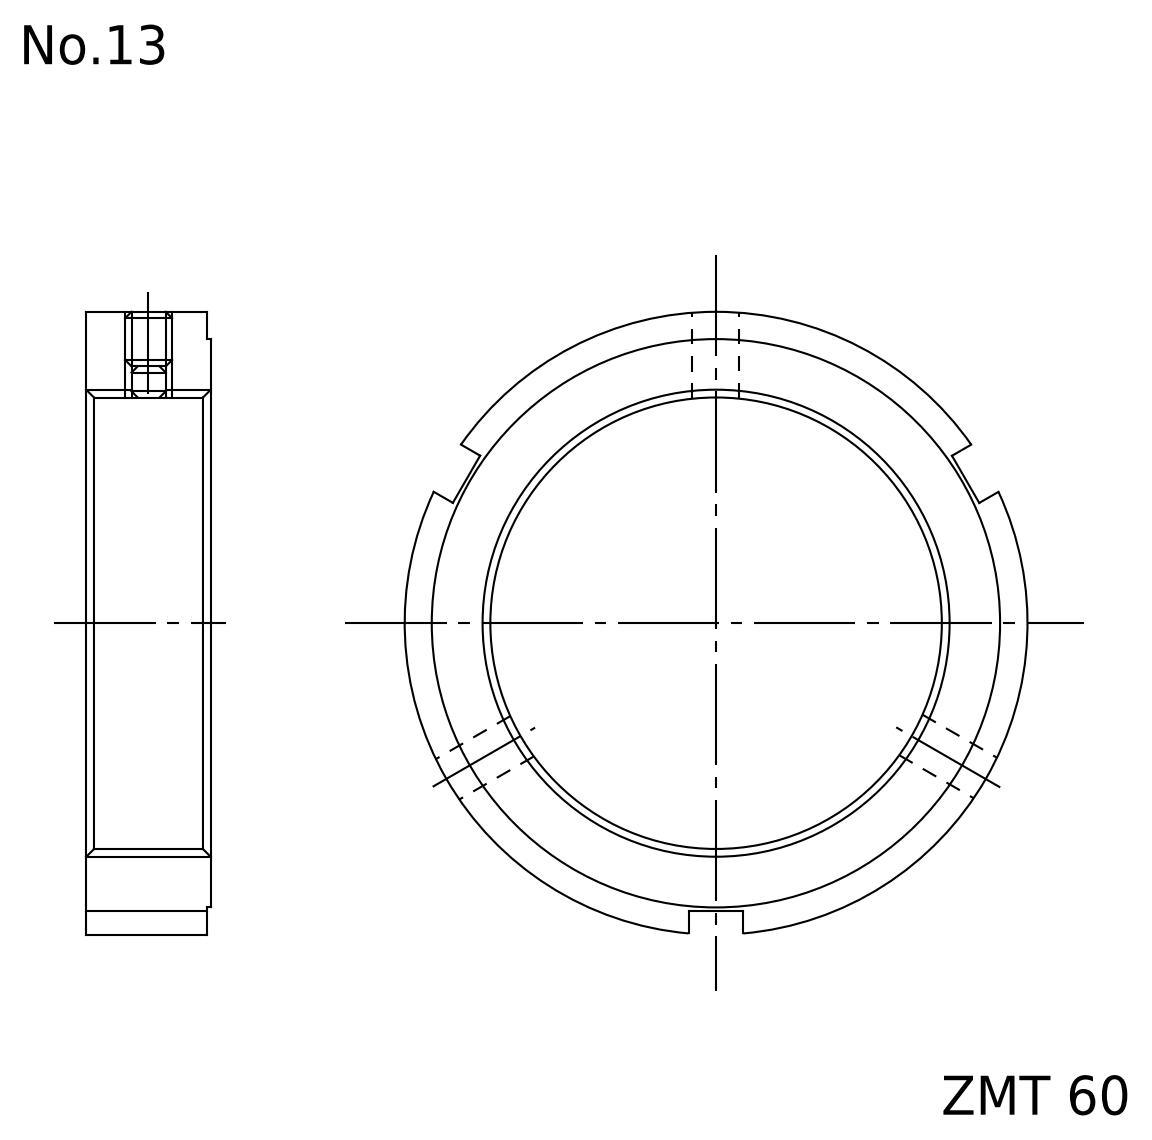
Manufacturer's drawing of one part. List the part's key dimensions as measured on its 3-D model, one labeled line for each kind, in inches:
Part name (STEP PRODUCT): FKD ZMT 60
STEP written by: Autodesk Inventor 2011 (AUTOMOTIVE_DESIGN)
Units: inches
Bodies: 1 solid, 20 faces (12 planar, 8 cylindrical, 0 other)
Overall size (bounding box): 3.15 × 3.144 × 0.63
Volume: 2.028 in³ · Surface area: 18.47 in²
Round holes (diameter × count): ⌀0.194 ×3, ⌀2.362 ×1
Round bosses / shafts (diameter × count): ⌀3.15 ×1, ⌀2.874 ×1
Main face-to-face distances: 0.63, 0.02, 0.61, 0.276
